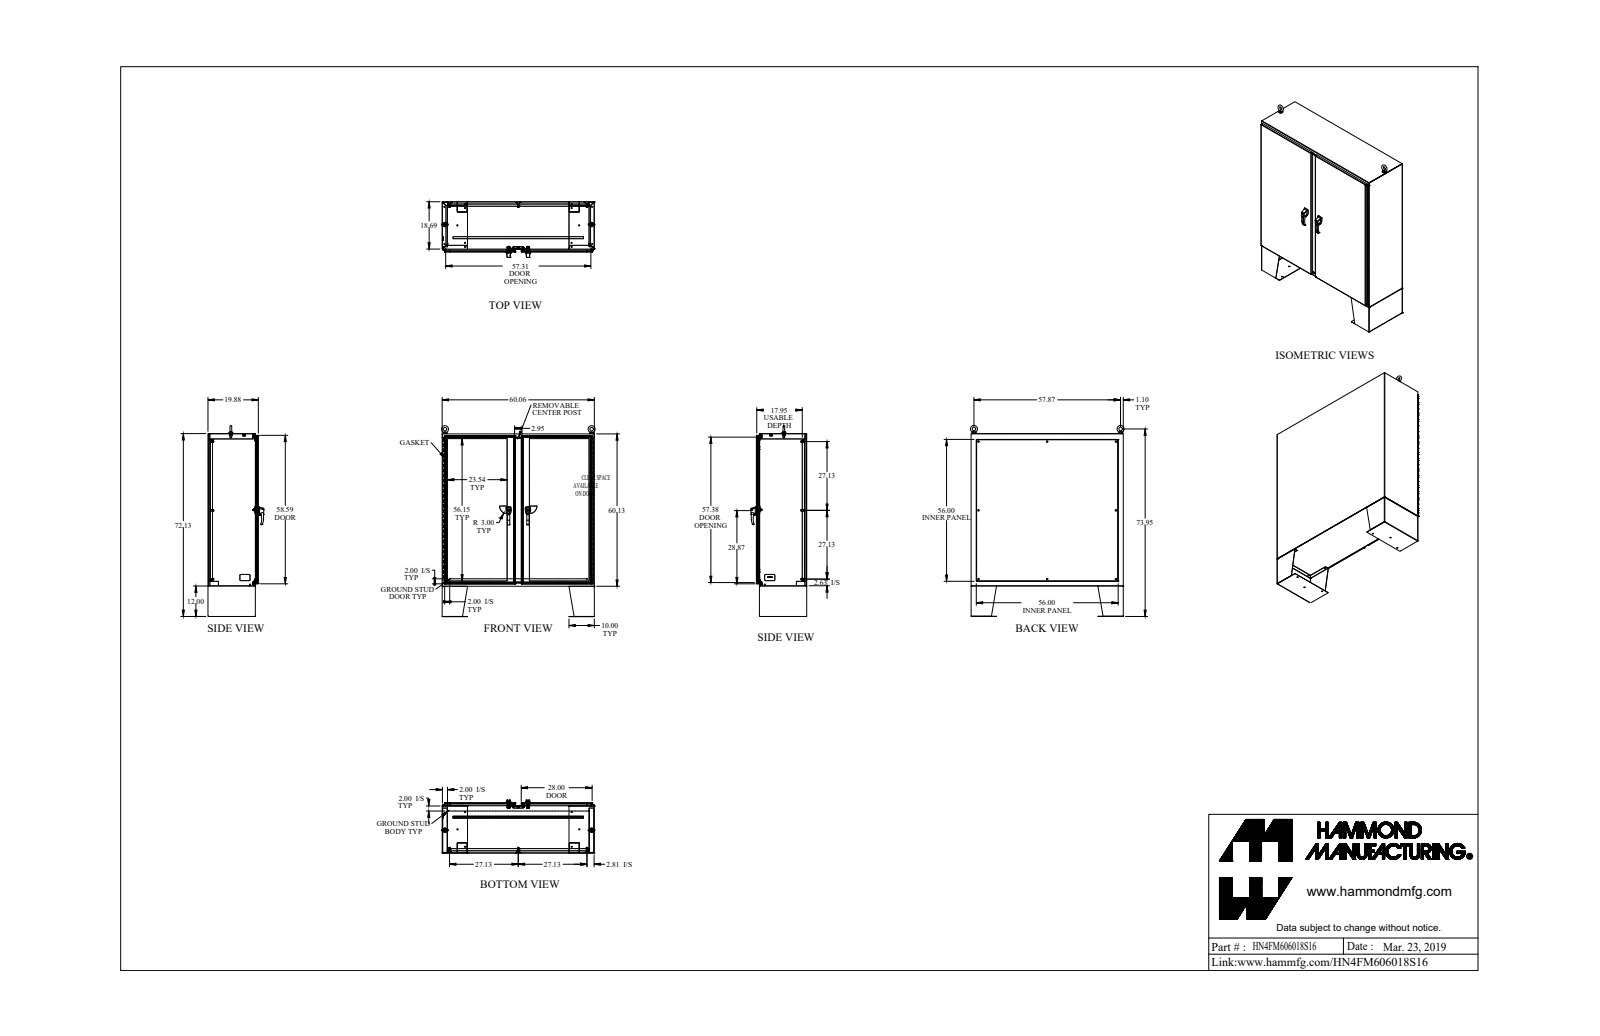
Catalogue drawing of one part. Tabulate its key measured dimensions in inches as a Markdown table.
| quantity | value |
| --- | --- |
| part name | HN4FM606018S16 |
| STEP written by | SolidWorks 2018 (AUTOMOTIVE_DESIGN) |
| units | inches |
| bodies | 134 solids, 3784 faces (1748 planar, 1675 cylindrical, 361 other) |
| overall size | 75.321 × 60.607 × 21.99 |
| volume | 1 921 in³ |
| surface area | 38 796 in² |
| round holes (diameter × count) | 0.304 × 20, 0.437 × 14, 0.307 × 8, 0.35 × 8, 0.563 × 8, 0.445 × 7, 0.25 × 6, 0.281 × 4, 0.313 × 4, 0.39 × 4, 0.201 × 3, 0.313 × 3 |
| round bosses / shafts (diameter × count) | 1 × 10, 0.65 × 8, 0.375 × 8, 0.332 × 8, 0.75 × 4, 0.625 × 4, 0.44 × 4, 0.37 × 4 |
| partial cylindrical surfaces (radius × count) | 0.5 × 33, 0.018 × 32, 0.125 × 32, 0.06 × 28, 0.048 × 27, 0.143 × 27, 0.03 × 12, 0.09 × 12 |
| main face-to-face distances | 0.095, 19.78, 19.685, 0.125, 19.875, 17.998, 1.782, 1.687, 18.093, 1.657 |
| hole center spacings | 6, 12, 18, 24, 54.25, 30, 58.491, 1.61 |
